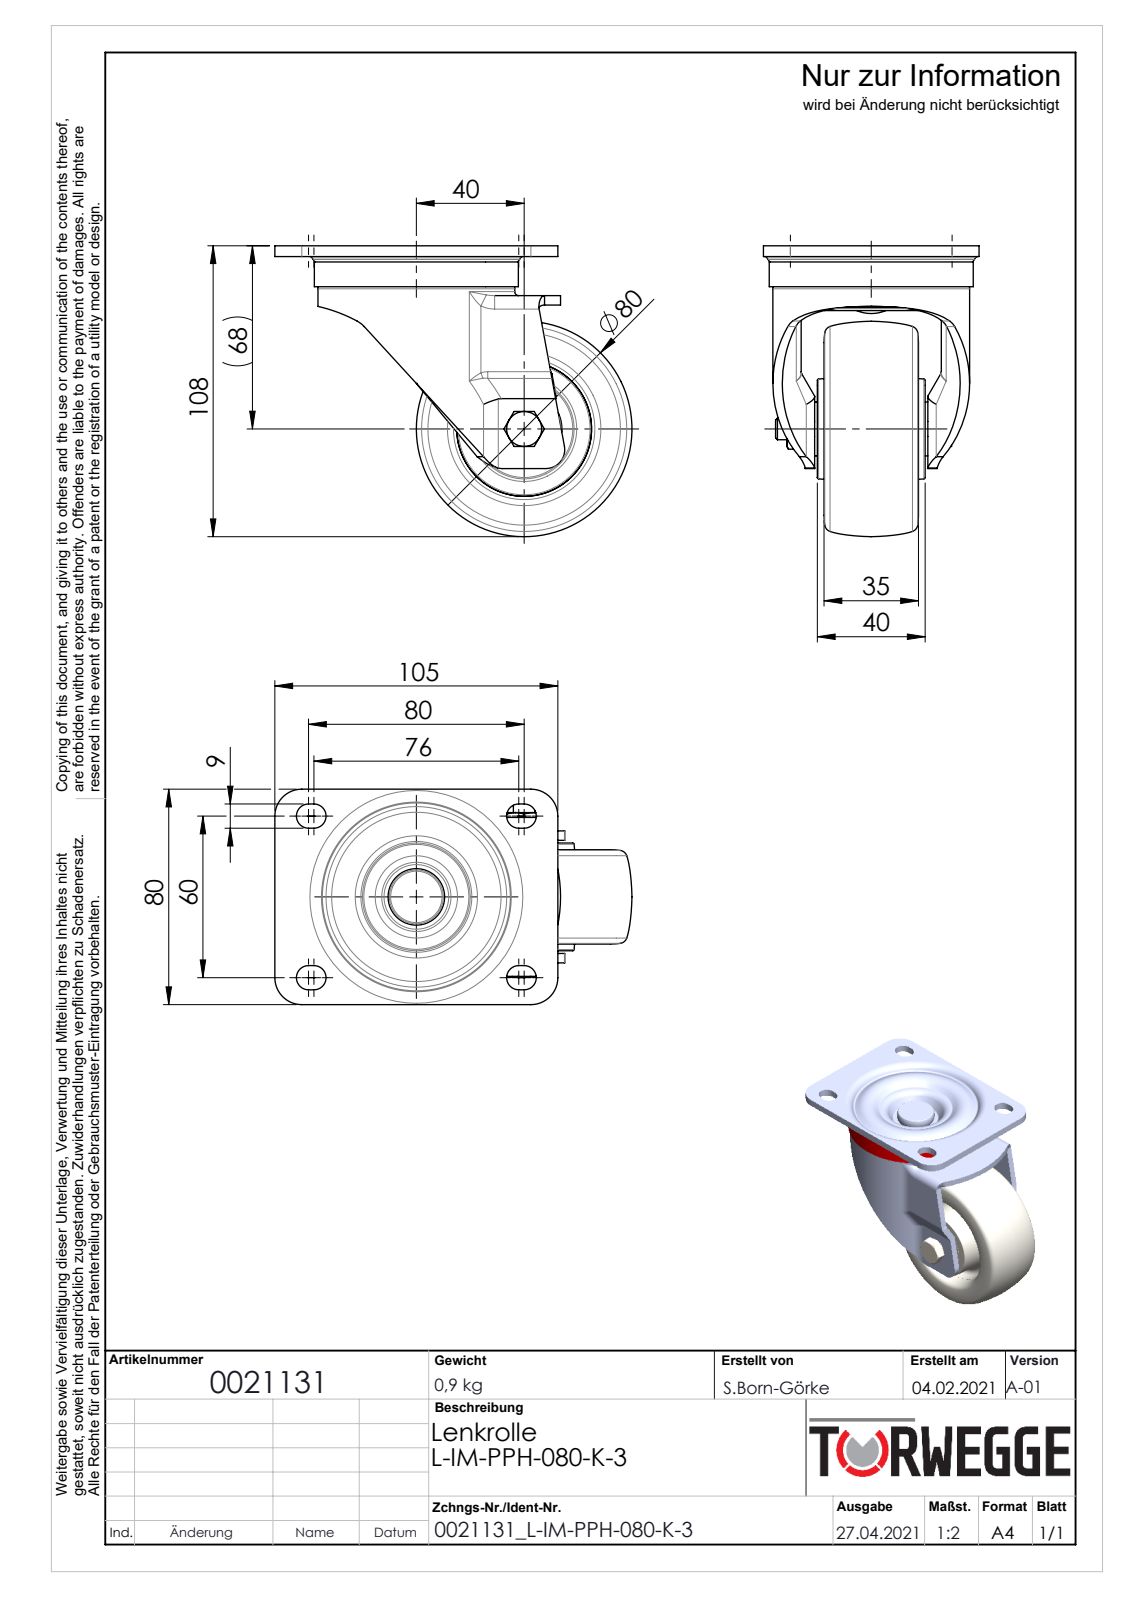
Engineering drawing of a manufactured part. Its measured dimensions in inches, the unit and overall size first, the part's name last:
Units: inches
Overall size (bounding box): 5.217 × 4.252 × 3.15
Round holes (diameter × count): ⌀0.268 ×1, ⌀0.315 ×1, ⌀0.323 ×1, ⌀0.472 ×1, ⌀0.488 ×1, ⌀0.492 ×1, ⌀0.661 ×1, ⌀0.906 ×1, ⌀0.913 ×1, ⌀1.102 ×1, ⌀1.382 ×1, ⌀1.398 ×1
Round bosses / shafts (diameter × count): ⌀2.98 ×1, ⌀2.874 ×1, ⌀2.067 ×1, ⌀0.827 ×1, ⌀0.787 ×1, ⌀0.591 ×1, ⌀0.512 ×1, ⌀0.492 ×1
Partial cylindrical surfaces — rounded edges, fillets, slot ends (radius × count): R0.011 ×8, R0.177 ×8, R0.006 ×7, R0.018 ×7, R0.025 ×4, R0.027 ×4, R0.059 ×4, R0.197 ×4
Main face-to-face distances: 0.157, 0.138, 0.039, 0.197, 1.988, 0.571, 1.181, 0.866, 0.551, 1.614
Volume: 15.55 in³ · Surface area: 203.4 in²
Bodies: 25 solids, 1027 faces (365 planar, 214 cylindrical, 448 other)
Part name (STEP PRODUCT): 0021131
STEP written by: SolidWorks 2020 (AUTOMOTIVE_DESIGN)
